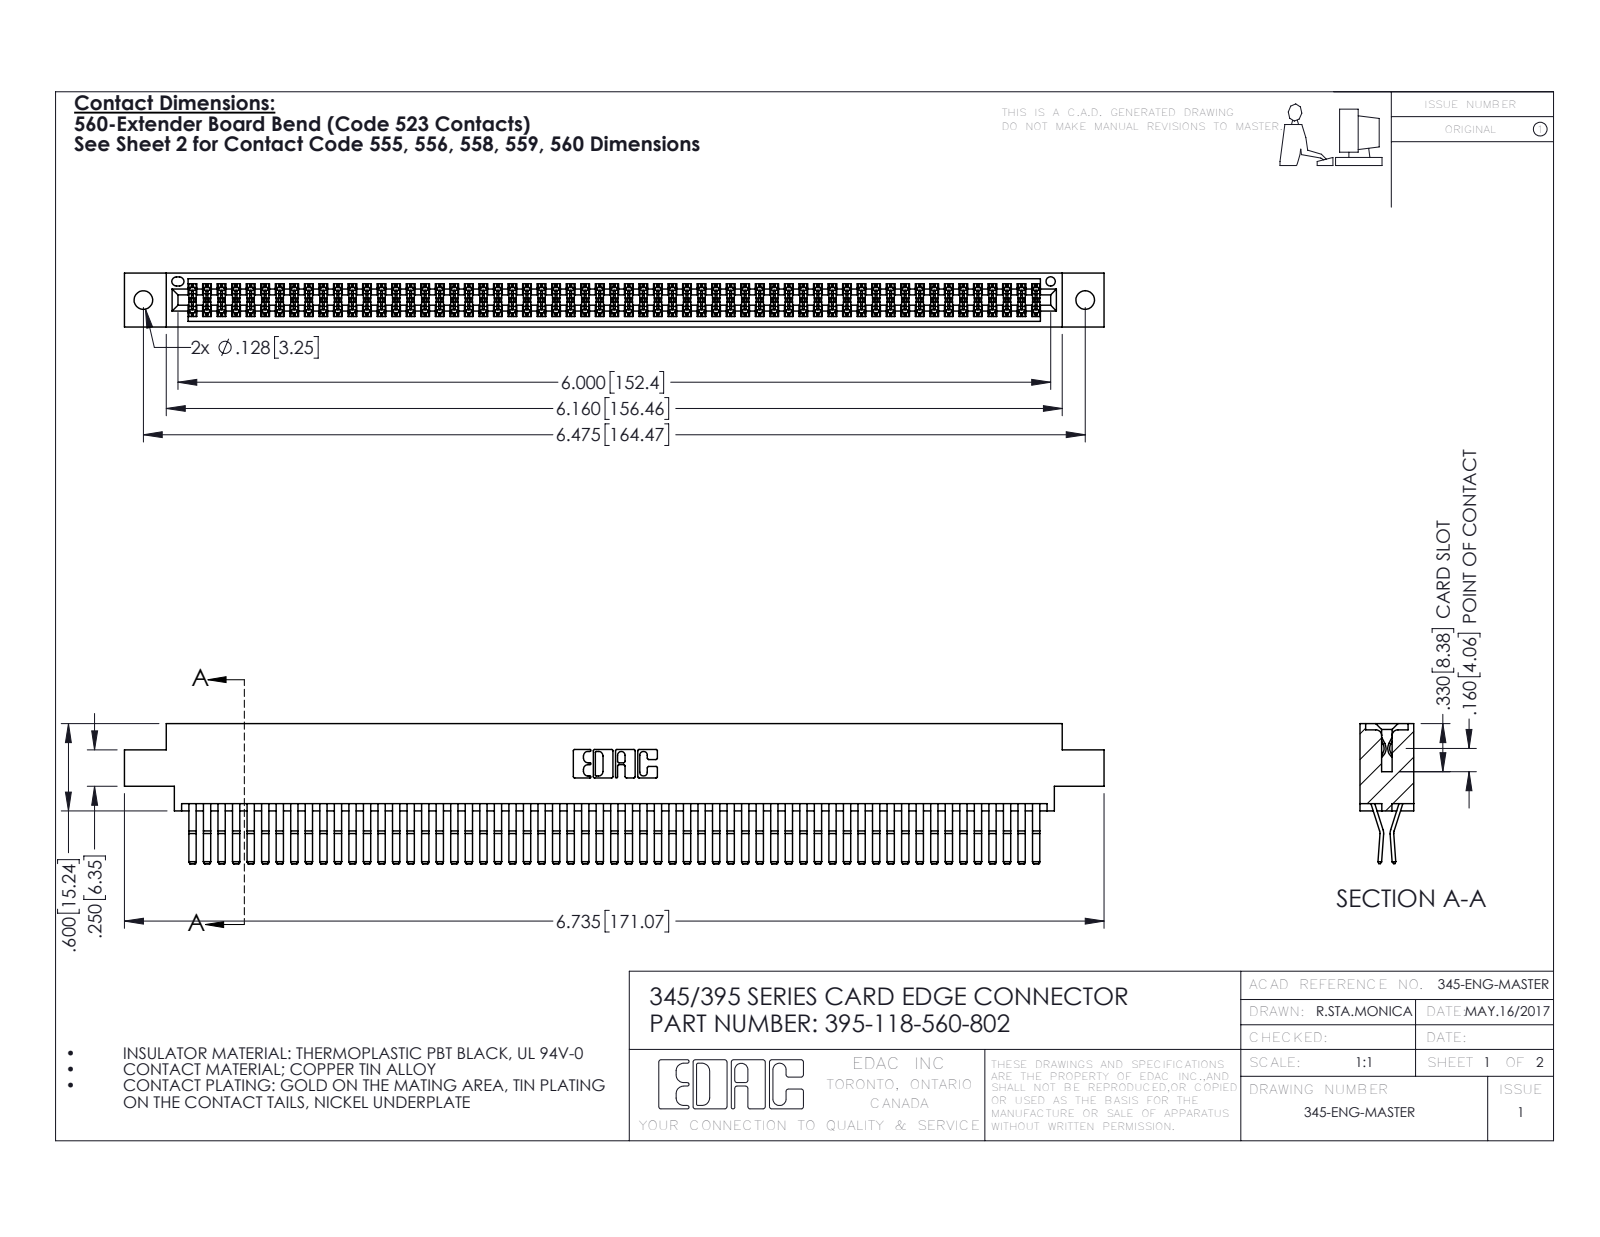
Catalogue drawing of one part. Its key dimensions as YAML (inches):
part_name: "345-292-001_560 Tail; 345 Part_0.170 Offset - 0.128 Dia; 395-118-560-802"
step_written_by: "SolidWorks 2016 (CONFIG_CONTROL_DESIGN)"
units: inches
bodies: {solids: 119, faces: 6266, planar: 3978, cylindrical: 2288, other: 0}
overall_size: [6.735, 0.962, 0.37]
volume: 1.062
surface_area: 43.26
round_holes:
  - {diameter: 0.128, count: 2}
  - {diameter: 0.064, count: 1}
partial_cylinders:
  - {radius: 0.006, count: 177}
  - {radius: 0.01, count: 22}
  - {radius: 0.007, count: 6}
  - {radius: 0.031, count: 6}
  - {radius: 0.026, count: 3}
  - {radius: 0.01, count: 2}
  - {radius: 0.014, count: 2}
  - {radius: 0.019, count: 2}
face_to_face_distances: [0.025, 0.298, 0.072, 0.37, 0.2, 0.098, 0.272, 0.225, 0.175, 0.149]
hole_center_spacings: [0.27, 6.239, 6.475]
